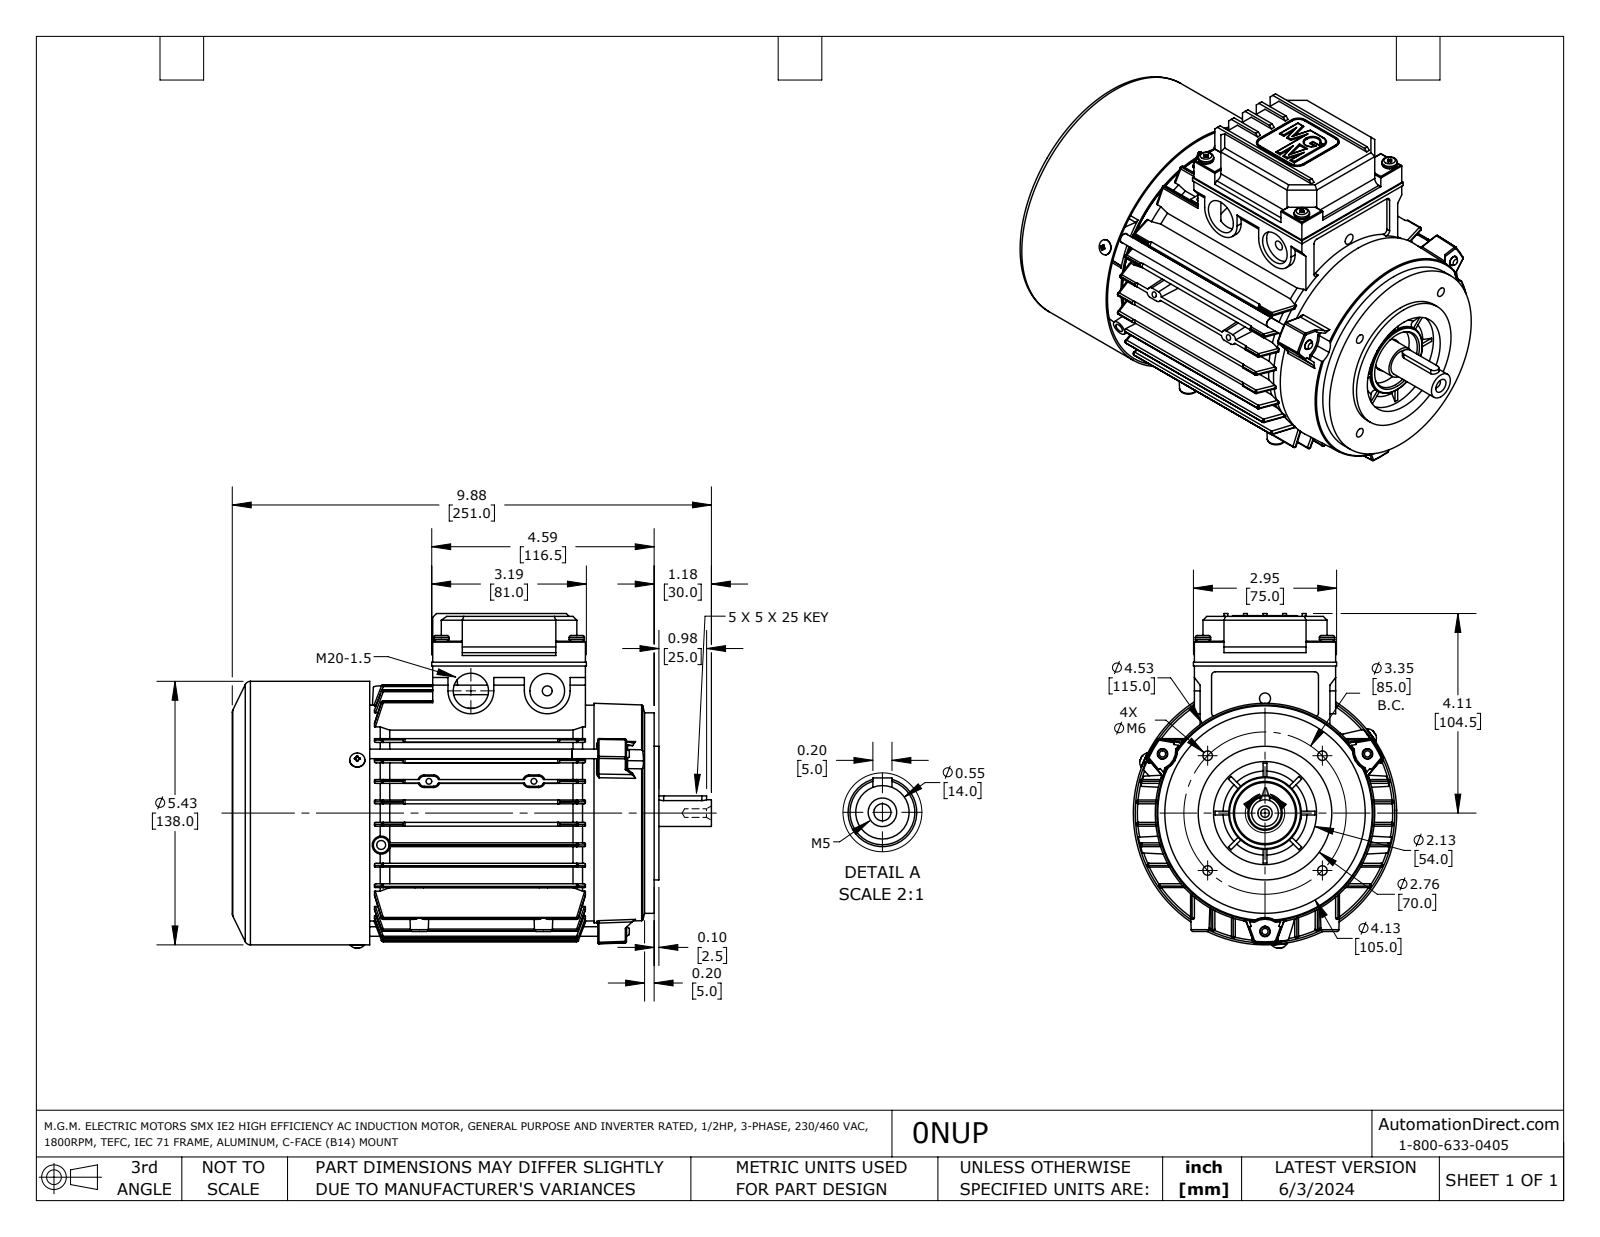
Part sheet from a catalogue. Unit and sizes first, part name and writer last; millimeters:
Units: millimetres
Overall size (bounding box): 251 × 175.3 × 138
Round holes (diameter × count): ⌀3 ×14, ⌀3.3 ×7, ⌀5.5 ×7, ⌀4 ×4, ⌀4.5 ×4, ⌀5 ×4, ⌀6 ×4, ⌀3.2 ×3, ⌀7 ×3, ⌀4.7 ×2, ⌀5.8 ×1, ⌀8 ×1
Round bosses / shafts (diameter × count): ⌀3 ×10, ⌀8 ×7, ⌀3.5 ×4, ⌀5 ×3, ⌀2 ×3, ⌀138 ×1, ⌀113 ×1, ⌀110.3 ×1
Partial cylindrical surfaces — rounded edges, fillets, slot ends (radius × count): R1 ×252, R0.9 ×60, R0.4 ×36, R0.2 ×32, R0.5 ×30, R0.1 ×16, R0.8 ×16, R0.6 ×12
Main face-to-face distances: 10.7, 2, 21.4, 43.8, 8.7, 54.6, 12.7, 33.1, 65.3, 45.8
Hole centre spacings: 12.1, 64.4, 14.5, 19, 28, 31, 31, 39.6
Volume: 526 400 mm³ · Surface area: 421 700 mm²
Bodies: 21 solids, 3316 faces (1029 planar, 1233 cylindrical, 1054 other)
Part name (STEP PRODUCT): 0NUP
STEP written by: SolidWorks 2021 (AUTOMOTIVE_DESIGN)
